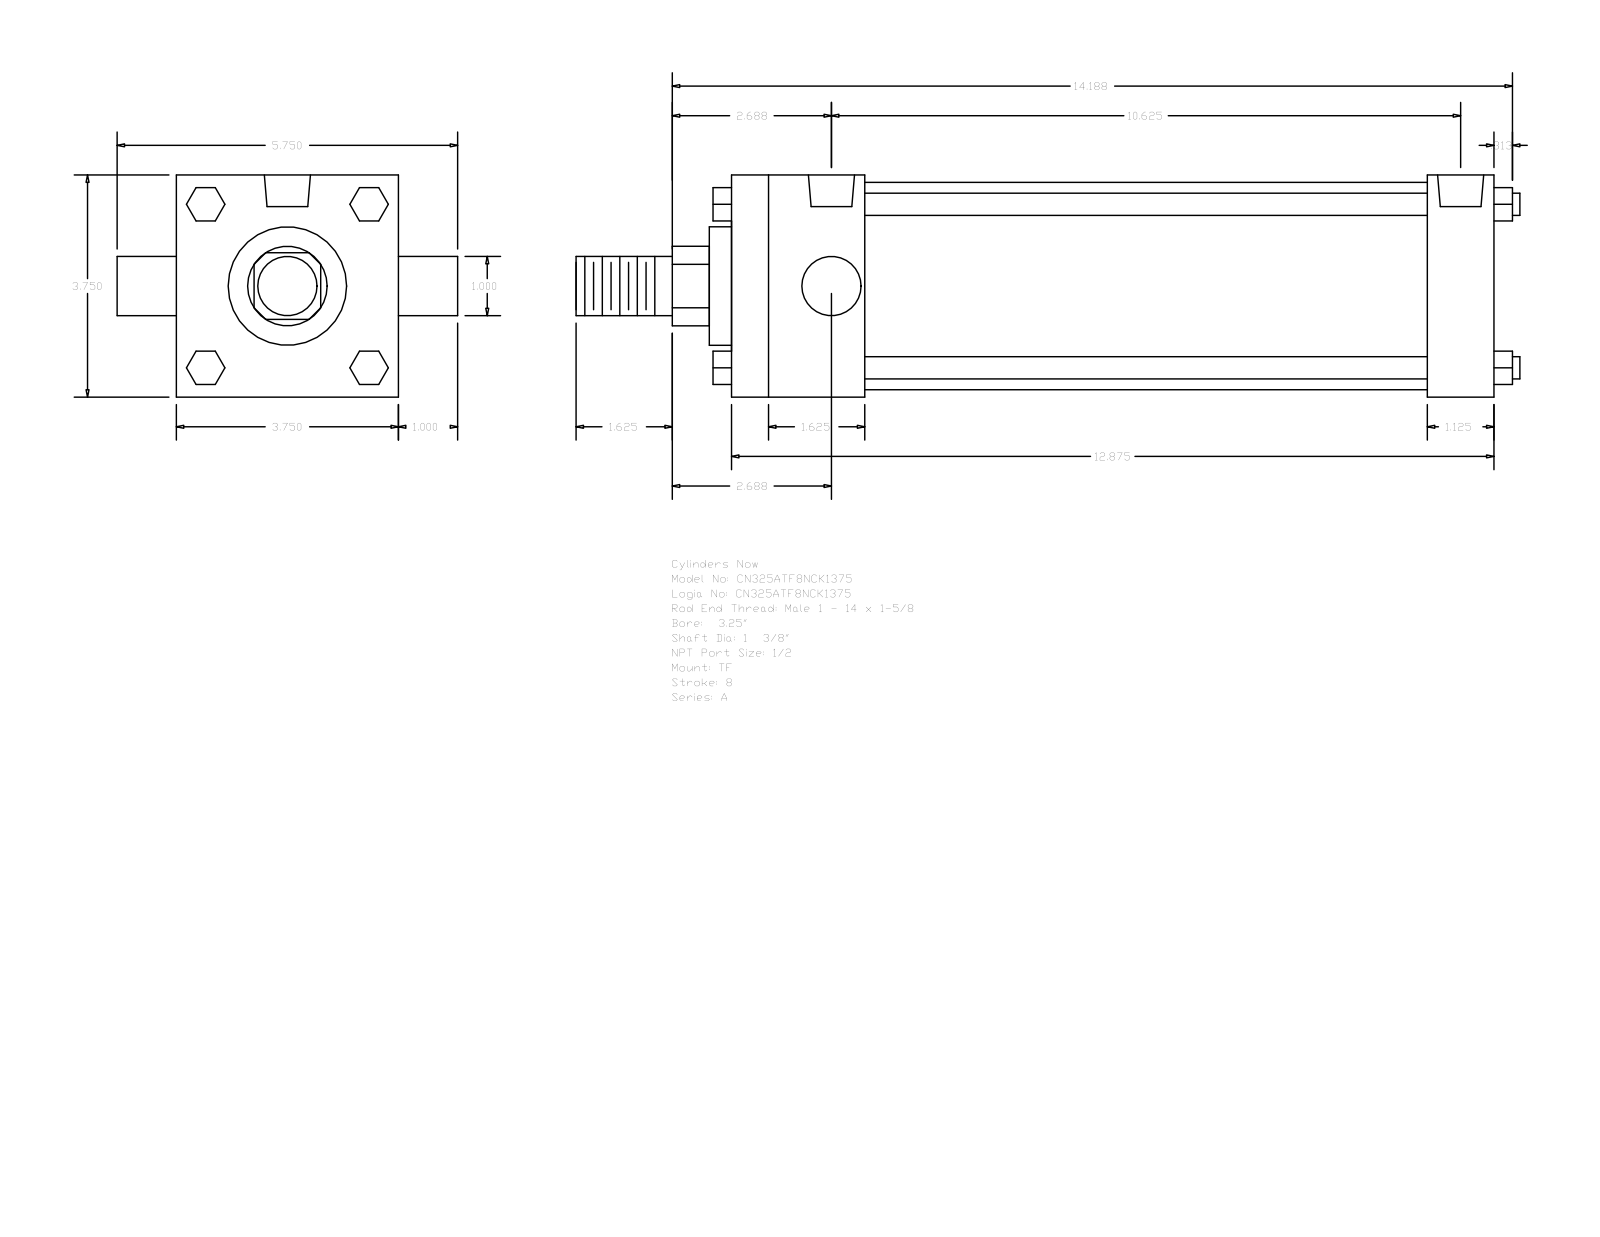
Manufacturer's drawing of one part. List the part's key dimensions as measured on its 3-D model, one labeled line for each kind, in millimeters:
Part name (STEP PRODUCT): A_TF__0325_1.375
STEP written by: GSSL Pune (CONFIG_CONTROL_DESIGN)
Units: millimetres
Bodies: 0 solids, 120 faces (92 planar, 28 cylindrical, 0 other)
Overall size (bounding box): 404.81 × 146.05 × 95.25
Round holes (diameter × count): ⌀8.73 ×3, ⌀19.77 ×2
Round bosses / shafts (diameter × count): ⌀9.53 ×4, ⌀25.4 ×2, ⌀88.9 ×1, ⌀50.8 ×1, ⌀34.92 ×1
Partial cylindrical surfaces — rounded edges, fillets, slot ends (radius × count): R17.06 ×1
Main face-to-face distances: 95.24, 327.03, 57.15, 28.58, 298.45, 241.3, 269.88, 66.67, 9.52, 307.97
Hole centre spacings: 3.18, 266.7, 263.52, 269.88
